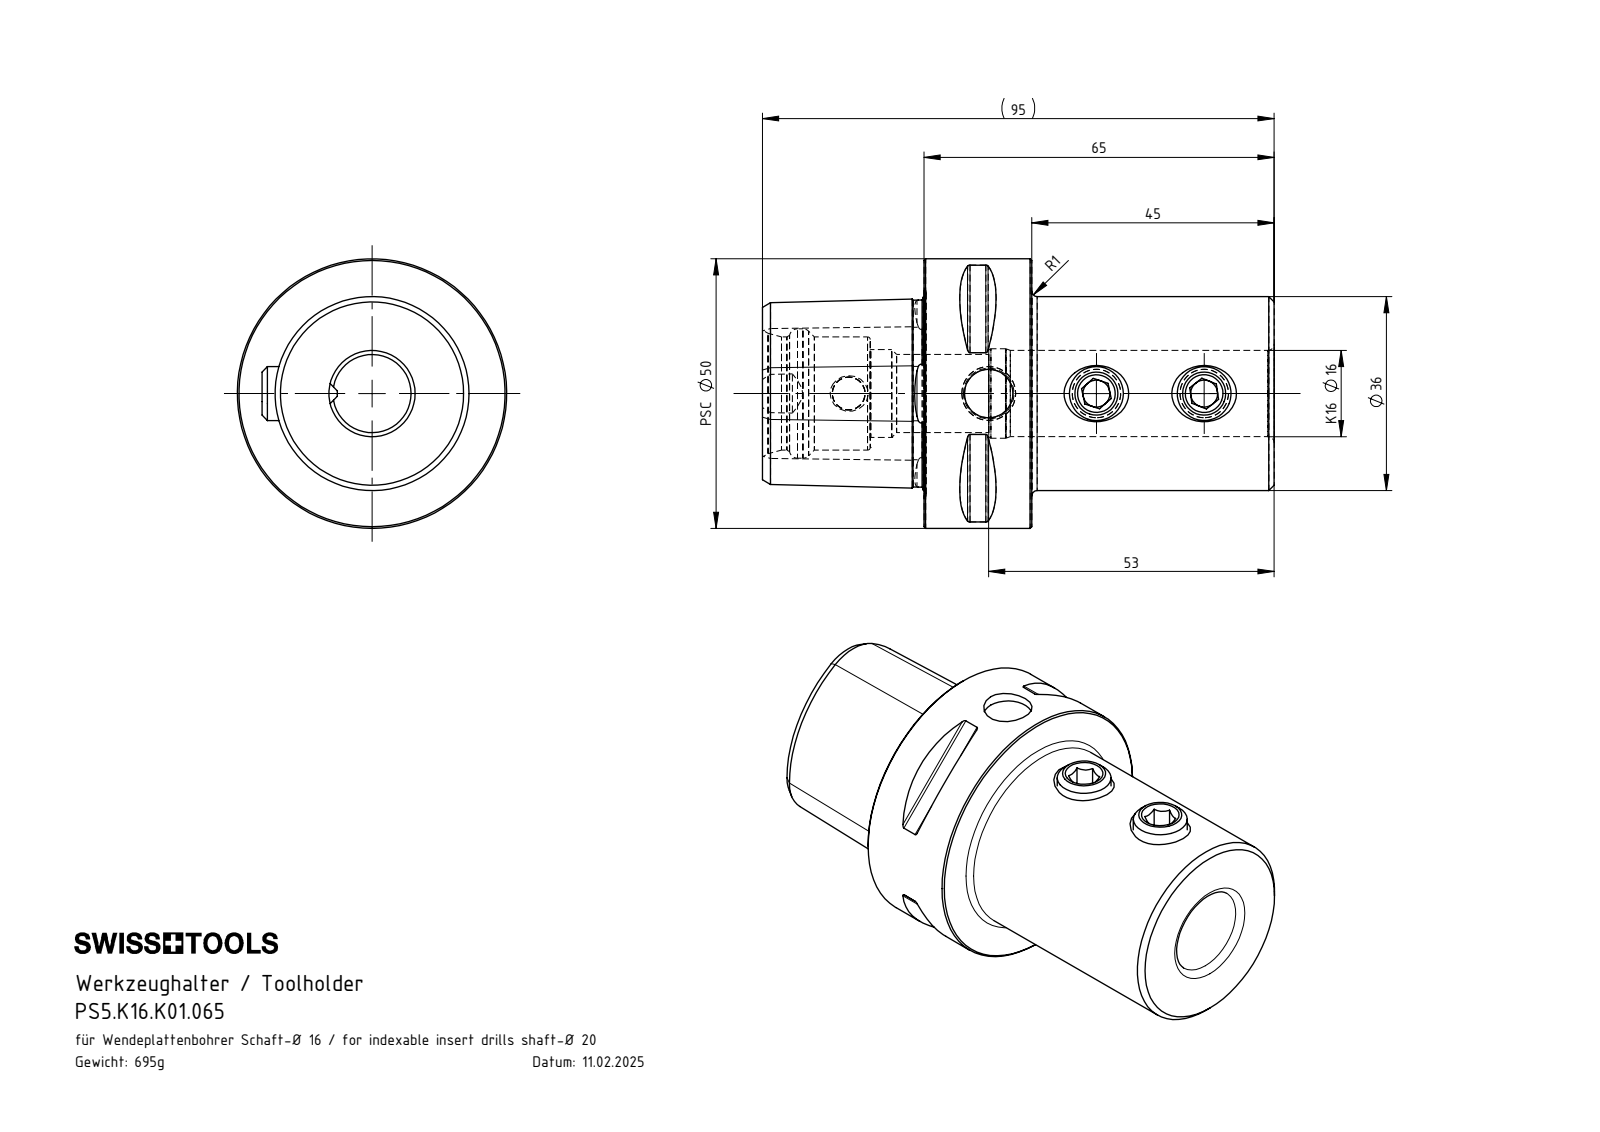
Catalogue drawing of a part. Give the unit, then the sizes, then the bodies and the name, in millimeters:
Units: millimetres
Overall size (bounding box): 95 × 50 × 50
Round holes (diameter × count): ⌀9 ×3, ⌀5 ×2, ⌀6.1 ×1, ⌀10 ×1, ⌀14.5 ×1, ⌀16 ×1, ⌀16.3 ×1, ⌀16.6 ×1, ⌀21 ×1, ⌀24 ×1
Round bosses / shafts (diameter × count): ⌀10 ×2, ⌀50 ×1, ⌀36 ×1
Partial cylindrical surfaces — rounded edges, fillets, slot ends (radius × count): R0.5 ×8, R5 ×1
Main face-to-face distances: 20, 65, 45, 30, 50, 95, 19.18, 44.4, 10, 75
Hole centre spacings: 20, 26, 40, 46, 66
Volume: 88 352 mm³ · Surface area: 21 699 mm²
Bodies: 3 solids, 208 faces (50 planar, 47 cylindrical, 111 other)
Part name (STEP PRODUCT): PS5-K16.K01.065_A; PS5.K16.K01.065; K16-ER1.010.010_A_PreviewCfg
STEP written by: SolidWorks 2022 (AUTOMOTIVE_DESIGN)
